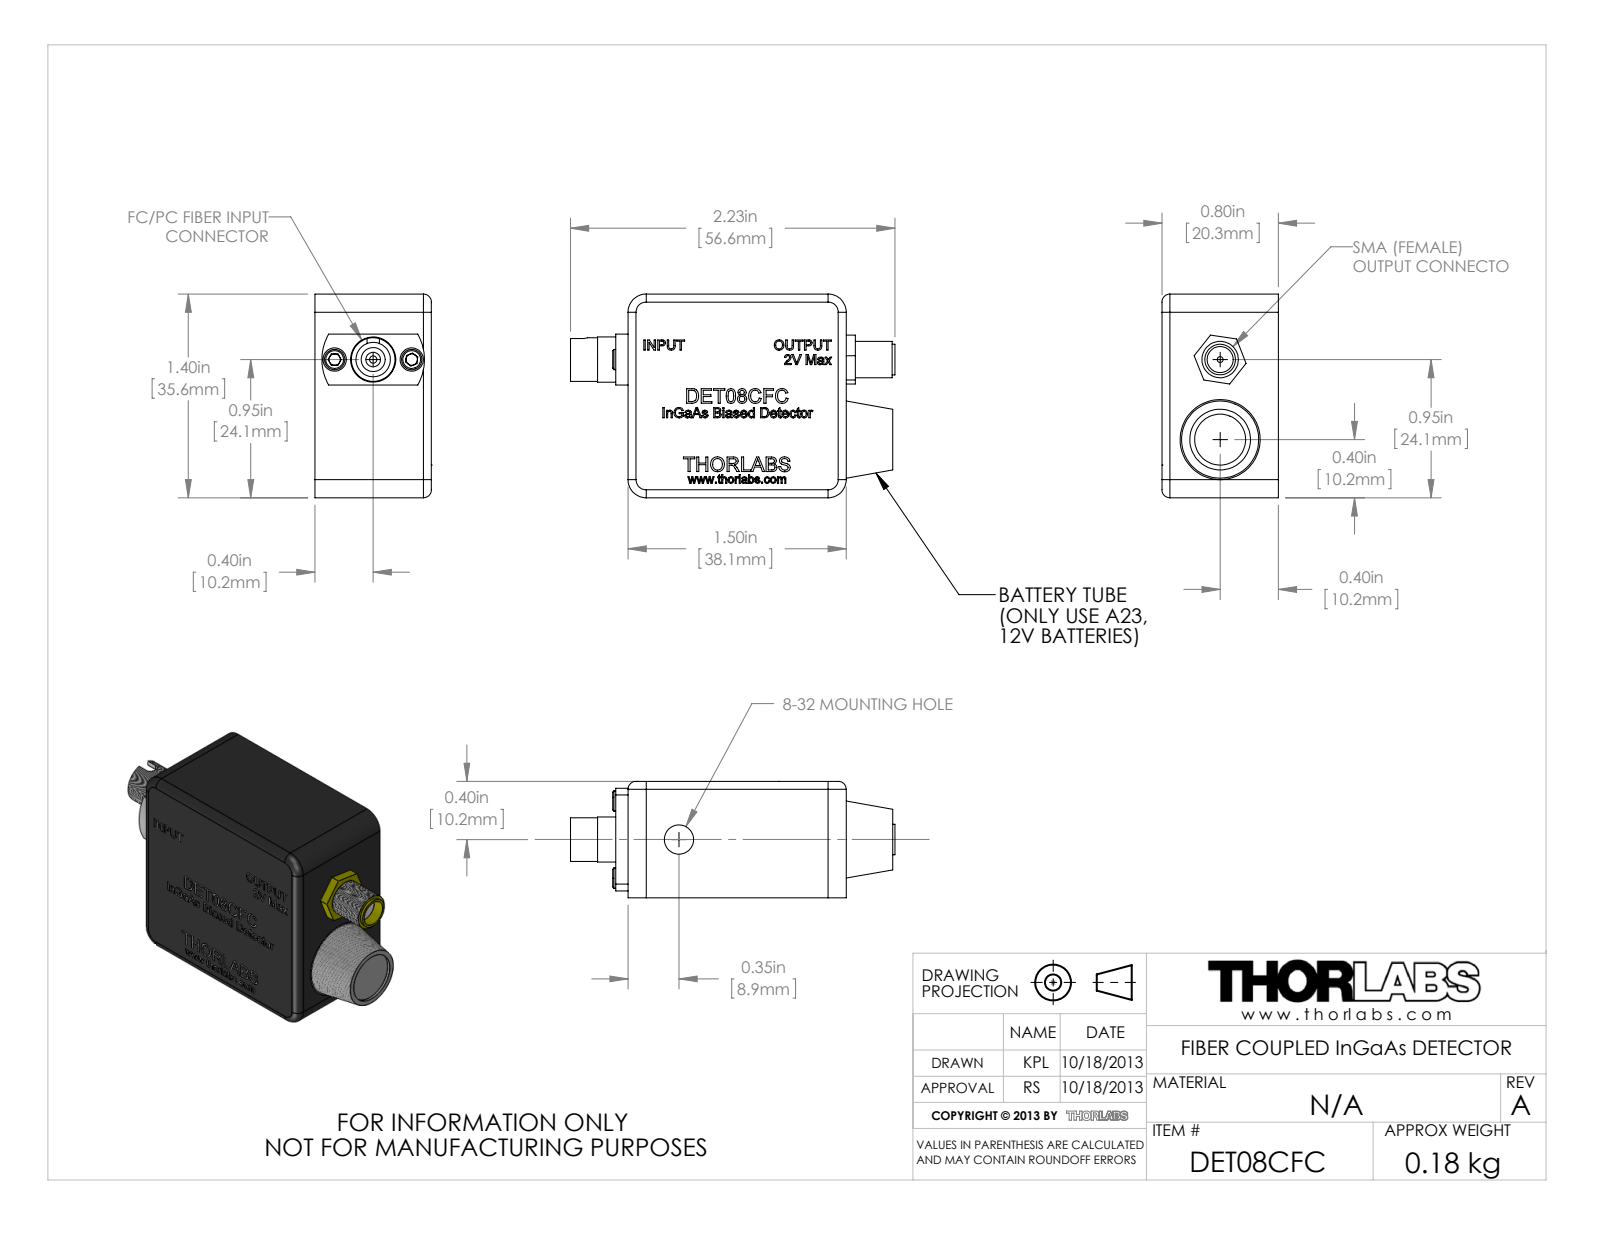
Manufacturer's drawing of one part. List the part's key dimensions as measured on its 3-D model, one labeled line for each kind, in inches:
Part name (STEP PRODUCT): TTN020103; PCB 002; PCB 001; OSI PD (+8 more)
STEP written by: SolidWorks 2012 (AUTOMOTIVE_DESIGN)
Units: inches
Bodies: 15 solids, 1743 faces (1021 planar, 190 cylindrical, 532 other)
Overall size (bounding box): 2.23 × 1.4 × 0.8
Volume: 1.115 in³ · Surface area: 23.62 in²
Round holes (diameter × count): ⌀0.07 ×6, ⌀0.096 ×4, ⌀0.14 ×4, ⌀0.125 ×3, ⌀0.085 ×2, ⌀0.16 ×2, ⌀0.017 ×1, ⌀0.04 ×1, ⌀0.05 ×1, ⌀0.05 ×1, ⌀0.079 ×1, ⌀0.1 ×1
Round bosses / shafts (diameter × count): ⌀0.086 ×6, ⌀0.143 ×4, ⌀0.017 ×3, ⌀0.14 ×2, ⌀0.472 ×1, ⌀0.432 ×1, ⌀0.327 ×1, ⌀0.31 ×1
Partial cylindrical surfaces — rounded edges, fillets, slot ends (radius × count): R0.125 ×12, R0.032 ×4, R0.055 ×4, R0.08 ×4, R0.095 ×4, R0.06 ×2, R0.1 ×2, R0.008 ×1
Main face-to-face distances: 0.063, 0.737, 0.8, 1.4, 0.5, 0.563, 0.237, 0.1, 0.55, 1.5
Hole centre spacings: 1.698, 1.15, 1.15, 1.25, 1.25, 0.265, 0.611, 0.872
